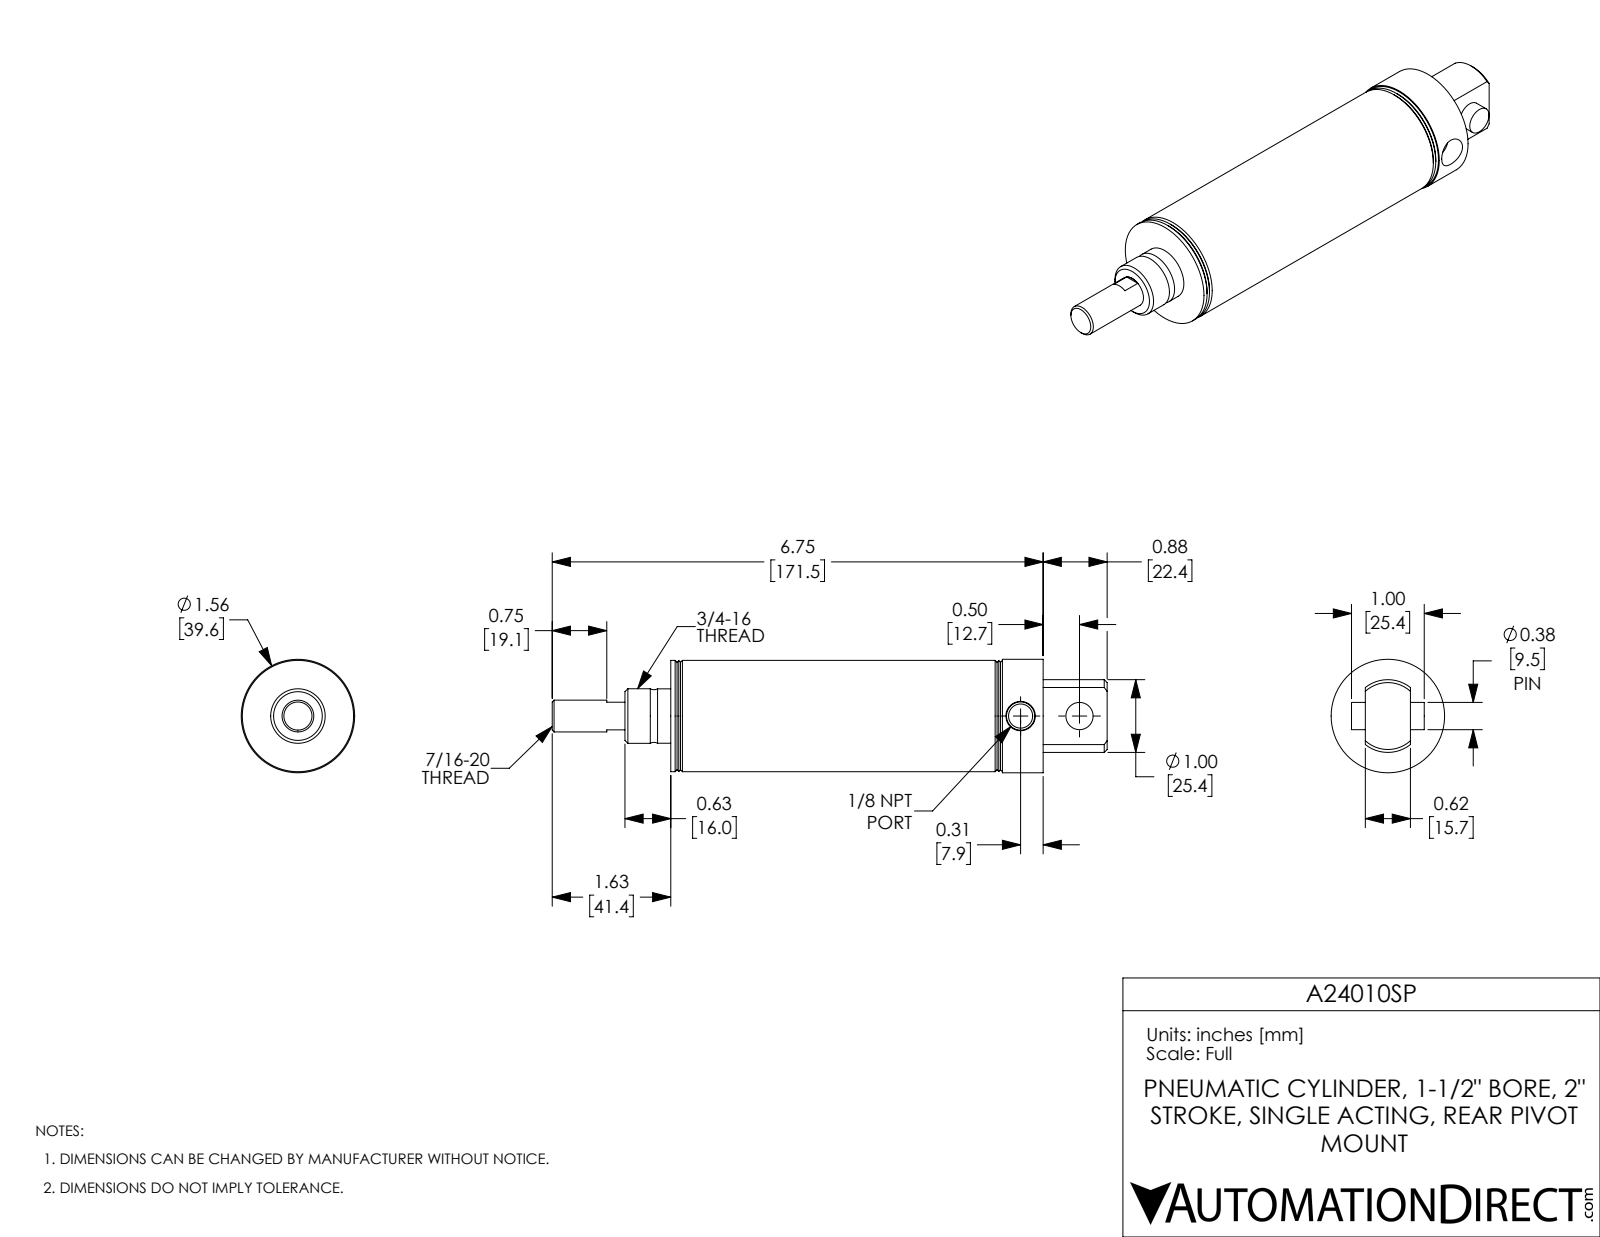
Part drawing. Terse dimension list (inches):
name: A24020SP-Rod; A24020SP-MainBody; A24020SP; A24020SP-PIN
written by: SolidWorks 2017 (AUTOMOTIVE_DESIGN)
unit: in
bodies: 3 solids, 78 faces (22 planar, 26 cylindrical, 30 other)
size: 7.63 × 1.56 × 1.56
volume: 7.125 in³; area: 65.16 in²
holes: 1× ⌀0.332, 1× ⌀0.375, 1× ⌀0.437, 1× ⌀1.5
bosses: 1× ⌀1.56, 1× ⌀1.53, 1× ⌀0.75, 1× ⌀0.747
rounds: 1× R0.5
face distances: 0.5, 2.5, 2, 3.655, 3.155, 1.155, 1.465, 1.965, 3.965, 5.12
hole spacings: 0.81
